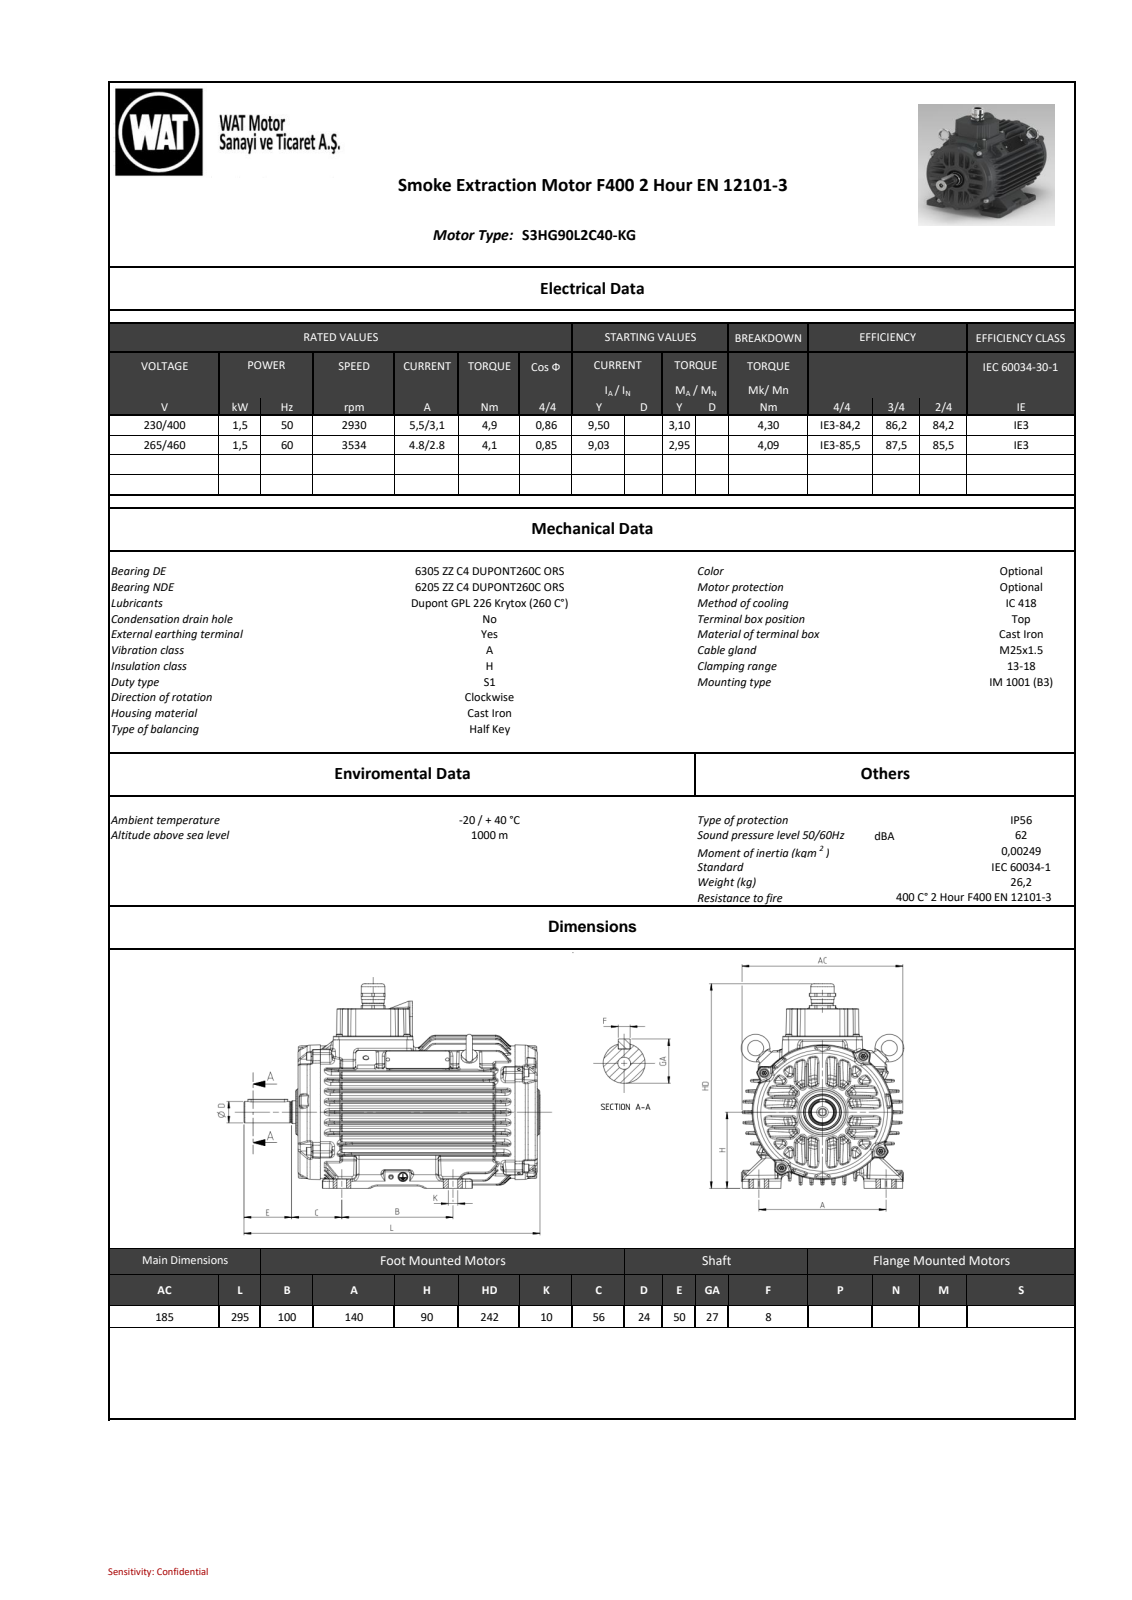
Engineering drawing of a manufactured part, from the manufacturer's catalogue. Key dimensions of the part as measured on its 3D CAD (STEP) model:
Part name (STEP PRODUCT): 26032C0836B7xhlo
STEP written by: SIEMENS PLM Software NX 11.0 (AUTOMOTIVE_DESIGN)
Units: millimetres
Bodies: 0 solids, 4025 faces (751 planar, 970 cylindrical, 2304 other)
Overall size (bounding box): 295.3 × 241.78 × 226.53
Round holes (diameter × count): ⌀2.5 ×2, ⌀4.2 ×2, ⌀6.8 ×1, ⌀8.4 ×1, ⌀18 ×1, ⌀32 ×1
Round bosses / shafts (diameter × count): ⌀8 ×4, ⌀20 ×3, ⌀9.2 ×3, ⌀8.28 ×3, ⌀5 ×3, ⌀62 ×1, ⌀29.59 ×1, ⌀28.14 ×1
Partial cylindrical surfaces — rounded edges, fillets, slot ends (radius × count): R1.5 ×423, R2 ×32, R1 ×30, R4 ×22, R0.5 ×19, R5 ×14, R3 ×6, R10 ×6
Main face-to-face distances: 12.04, 231.53, 236.03, 4.5, 39.98, 190.53, 41, 45.5, 159.56, 199.54
Hole centre spacings: 75
